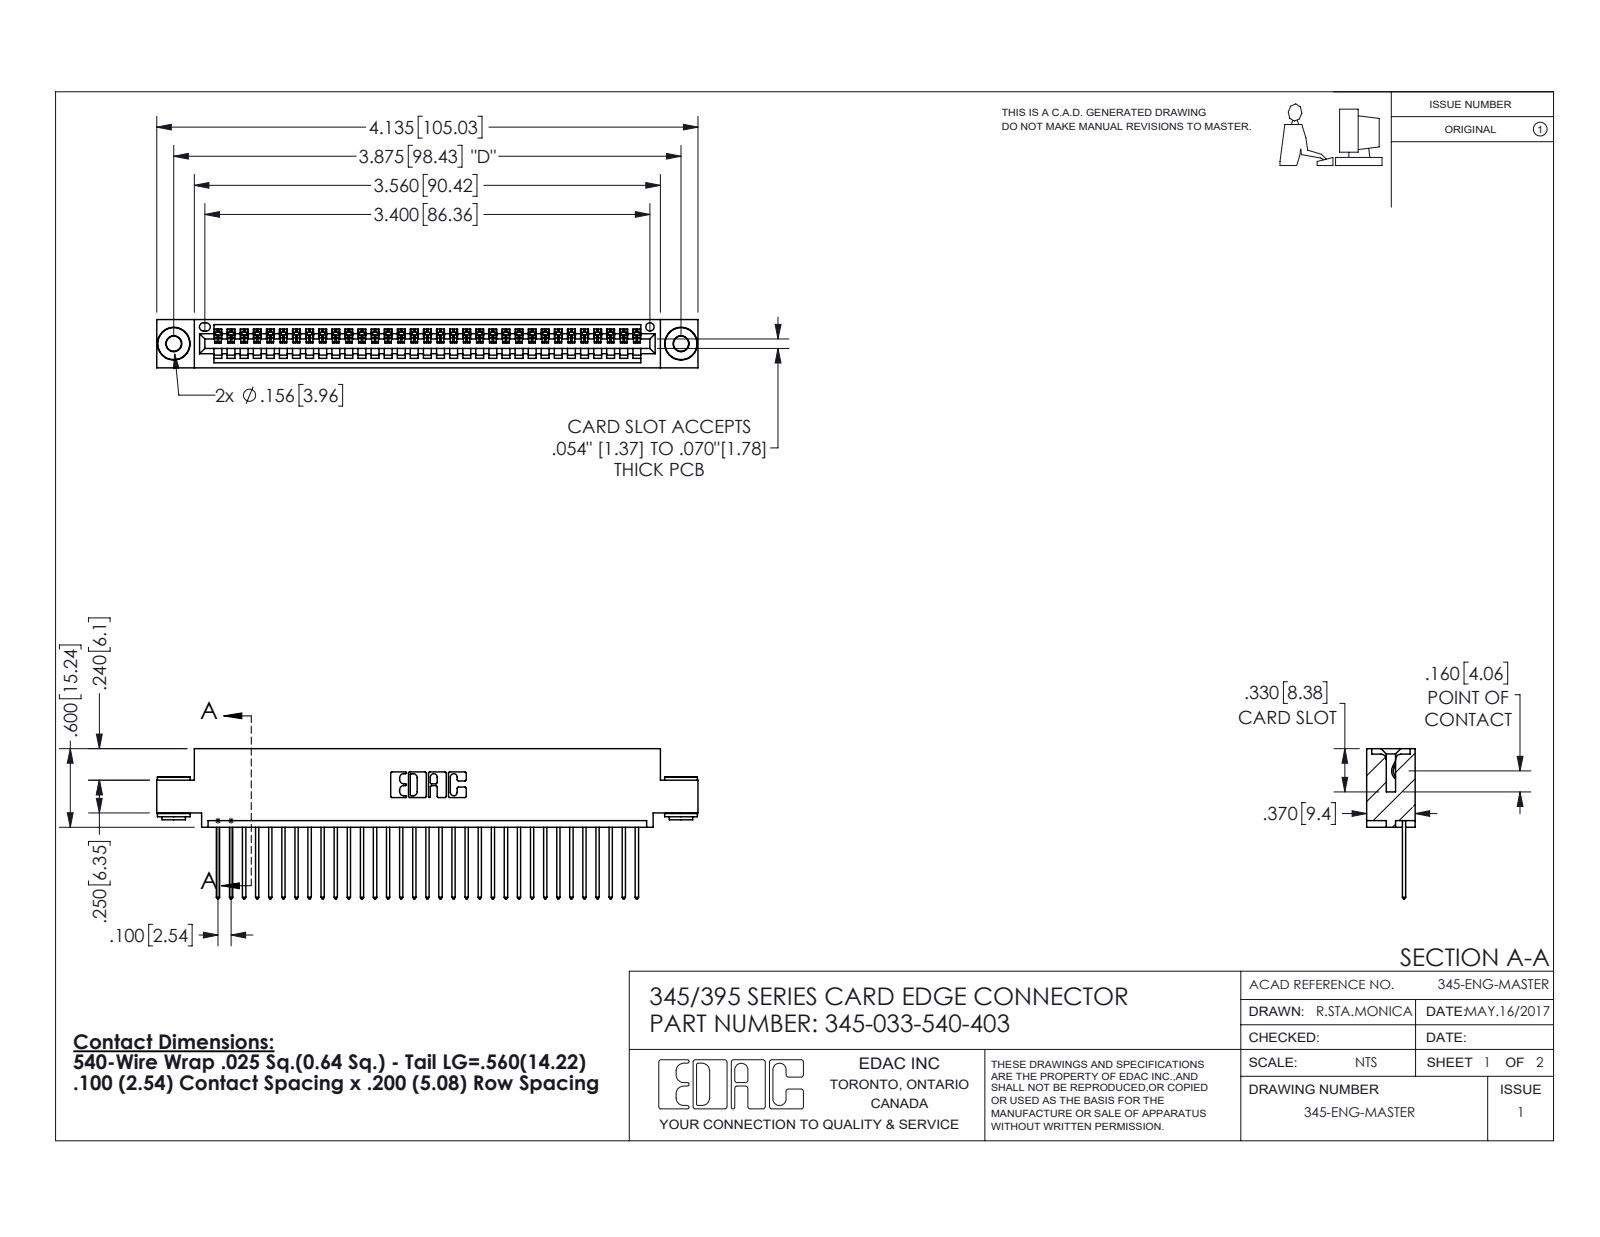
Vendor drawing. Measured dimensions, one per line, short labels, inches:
name: 345-033-540-403; 345-250-002_345-250-002-102; 345-292-001_345-293-140; 345 Part_0.110 Offset - 0.156 Dia-TH
written by: SolidWorks 2016 (CONFIG_CONTROL_DESIGN)
unit: in
bodies: 36 solids, 2082 faces (1414 planar, 660 cylindrical, 8 other)
size: 4.135 × 1.147 × 0.37
volume: 0.604 in³; area: 21.15 in²
holes: 2× ⌀0.116, 2× ⌀0.156, 1× ⌀0.064
bosses: 2× ⌀0.25, 2× ⌀0.18, 2× ⌀0.136
rounds: 66× R0.006, 66× R0.01, 22× R0.01, 6× R0.007, 6× R0.031, 3× R0.026, 2× R0.031, 2× R0.04
face distances: 0.072, 0.298, 0.37, 0.025, 0.2, 0.098, 0.272, 0.225, 0.149, 0.072
hole spacings: 0.27, 3.64, 3.875
